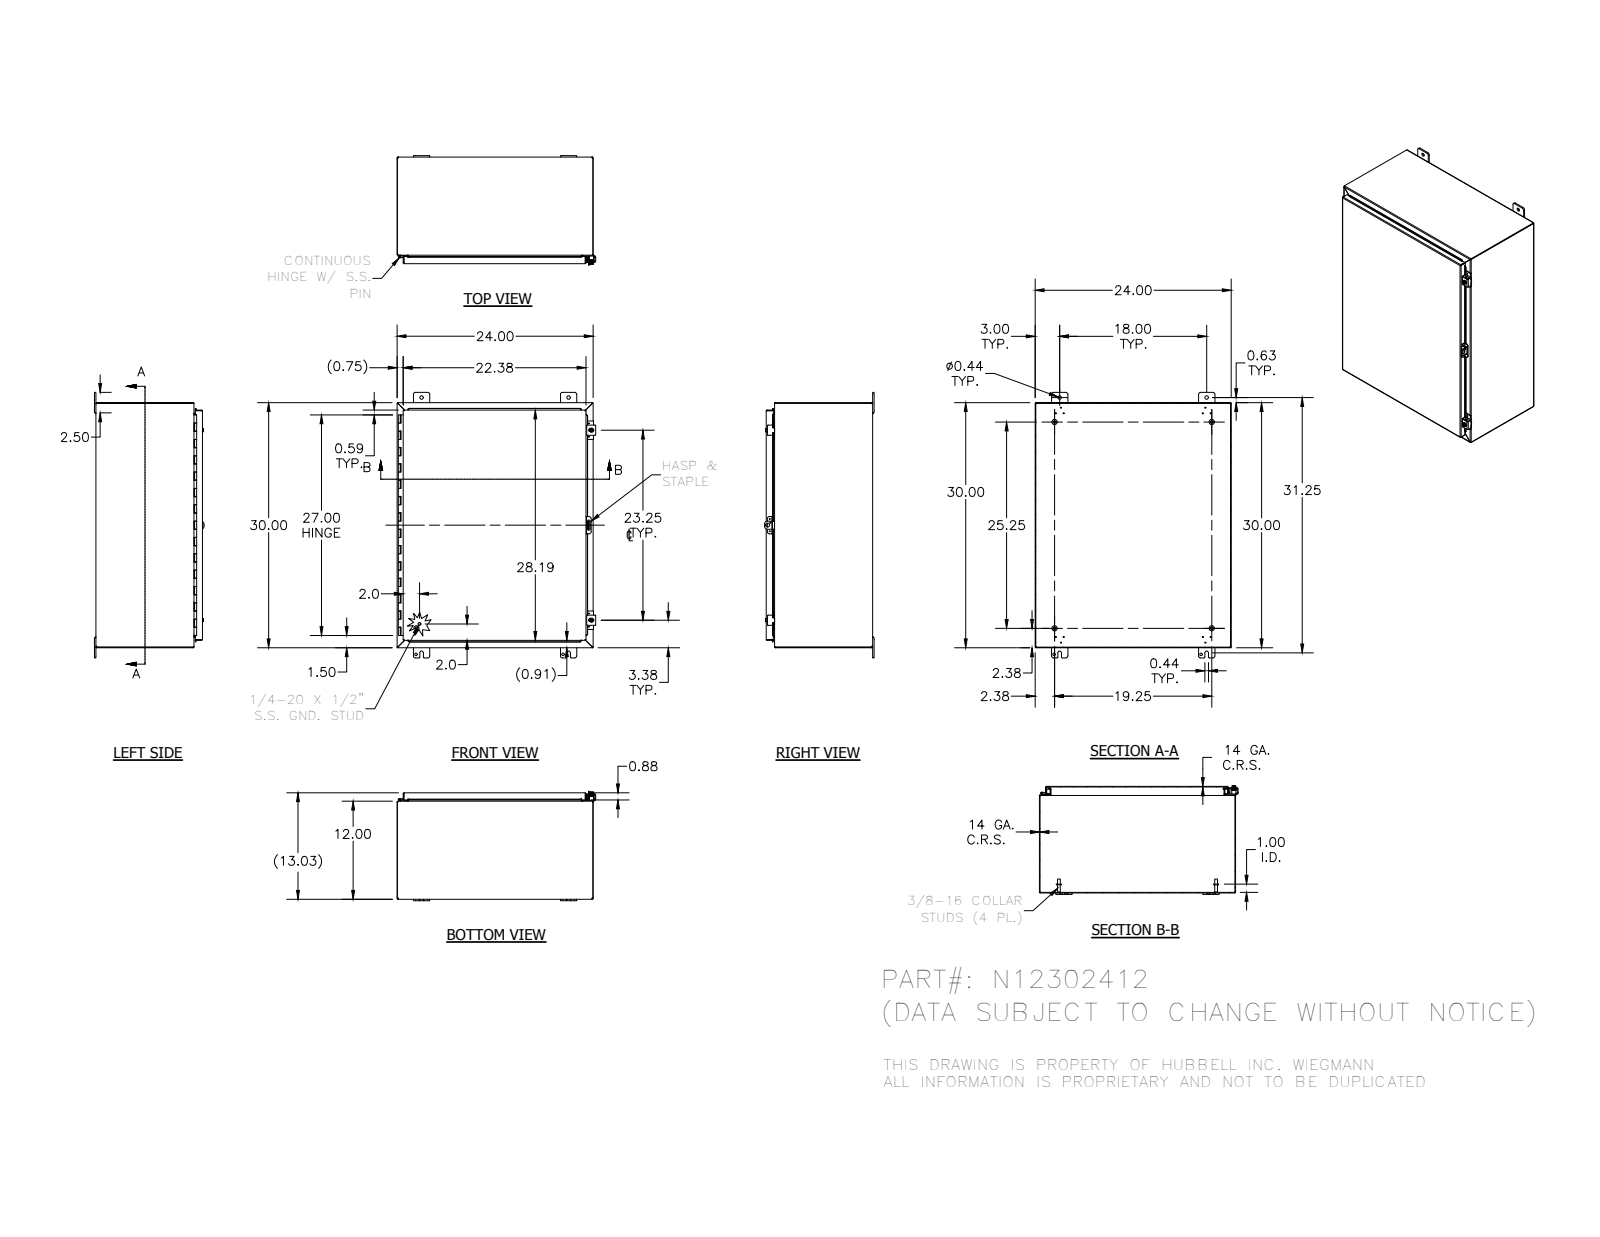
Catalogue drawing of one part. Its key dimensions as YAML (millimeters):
part_name: "N12302412; 34840; 38420; N12302412BKP (+8 more)"
step_written_by: "Autodesk Inventor 2012 (AUTOMOTIVE_DESIGN)"
units: millimeters
bodies: {solids: 27, faces: 1033, planar: 566, cylindrical: 350, other: 117}
overall_size: [825.5, 617.5, 340.6]
volume: 3897000
surface_area: 4041000
round_holes:
  - {diameter: 3, count: 12}
  - {diameter: 2.8, count: 7}
  - {diameter: 8, count: 4}
  - {diameter: 11.1, count: 4}
  - {diameter: 5.4, count: 2}
  - {diameter: 7.1, count: 2}
  - {diameter: 7.6, count: 2}
  - {diameter: 3.2, count: 1}
  - {diameter: 4, count: 1}
  - {diameter: 12.7, count: 1}
round_bosses_or_shafts:
  - {diameter: 15.9, count: 4}
  - {diameter: 8.4, count: 4}
  - {diameter: 6.4, count: 4}
  - {diameter: 13.2, count: 2}
  - {diameter: 12.7, count: 2}
  - {diameter: 8.9, count: 2}
  - {diameter: 2.9, count: 2}
  - {diameter: 8.6, count: 1}
partial_cylinders:
  - {radius: 0.8, count: 27}
  - {radius: 1.6, count: 25}
  - {radius: 3.2, count: 25}
  - {radius: 6.4, count: 25}
  - {radius: 0.8, count: 23}
  - {radius: 2.7, count: 23}
  - {radius: 1.8, count: 8}
  - {radius: 2.5, count: 4}
face_to_face_distances: [1.9, 329.2, 607.7, 327.3, 331, 760.1, 605.8, 609.6, 762, 758.2]
hole_center_spacings: [457.2, 19.3, 21.3, 23.9, 24.6, 50.7, 441.2, 465.8]
